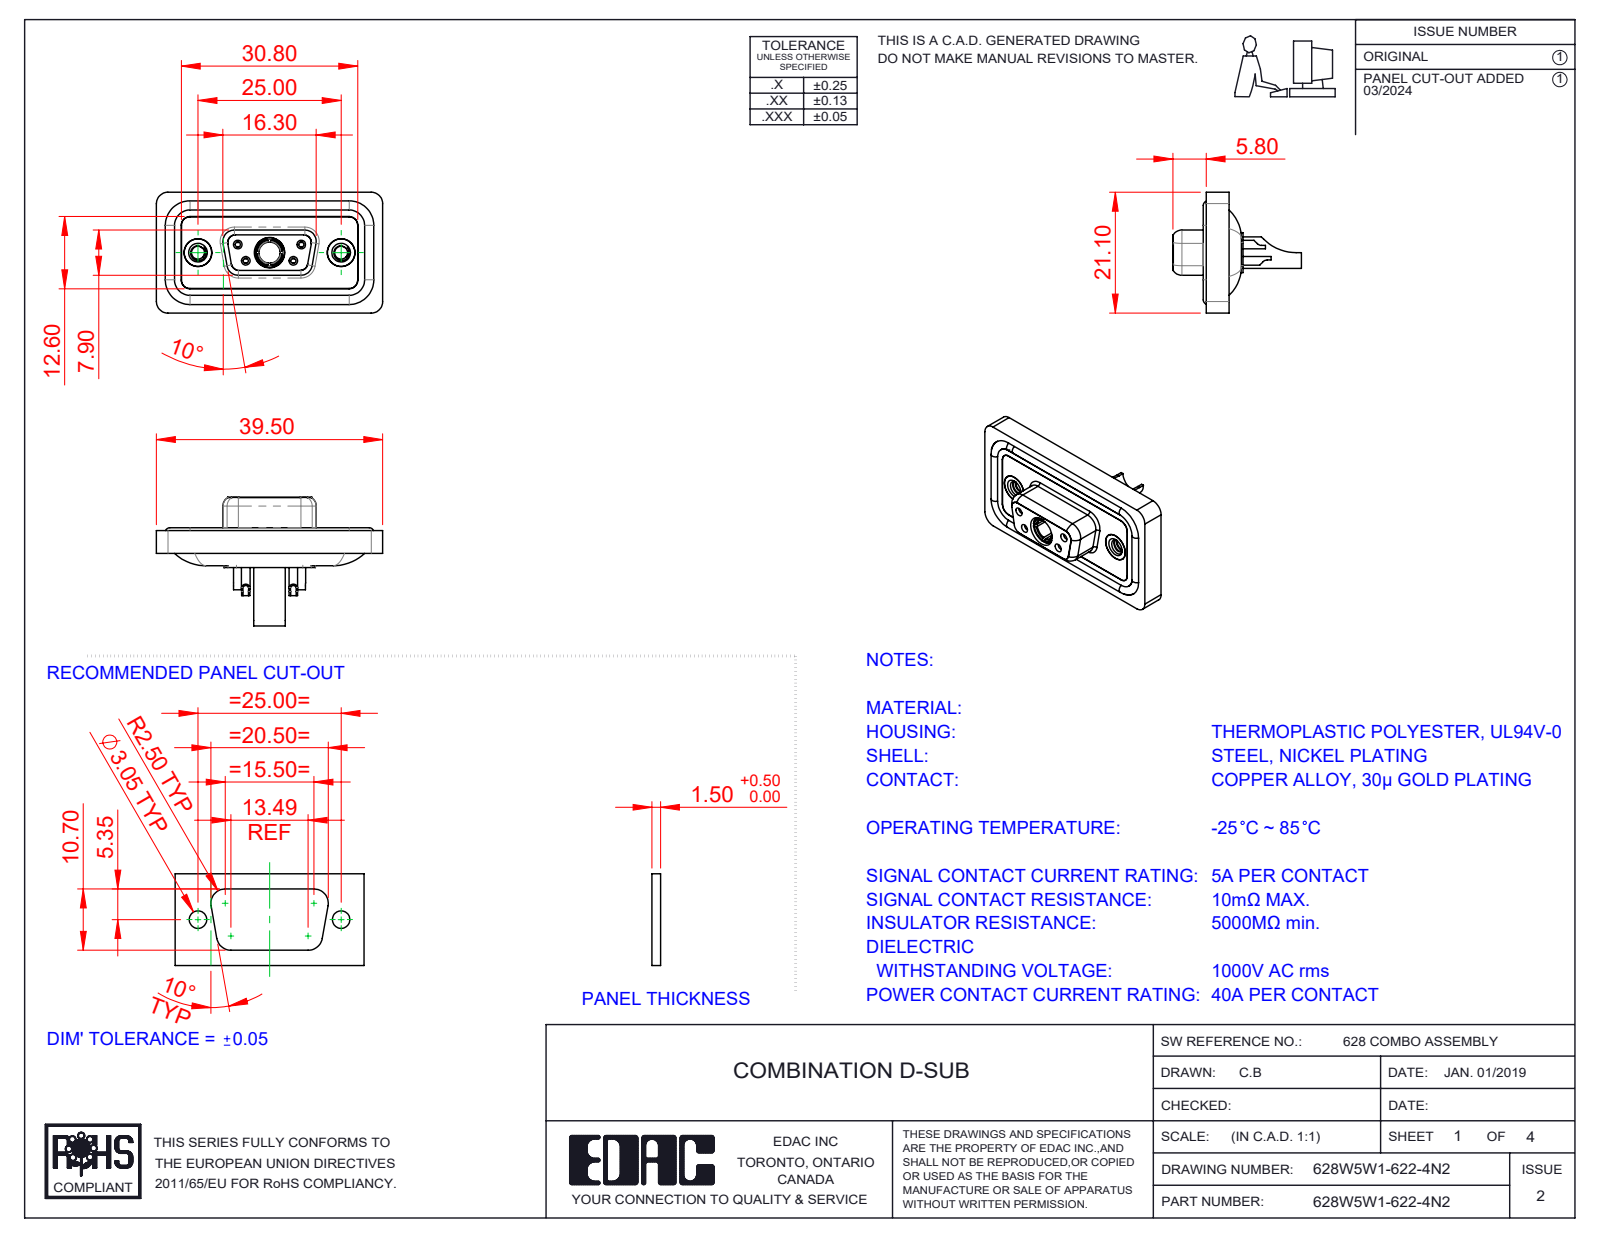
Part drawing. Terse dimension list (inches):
name: 628Combo Shell Front_09 Contacts; 628Combo Housing_5W1; 628Combo Shell Rear_09 Contacts; Power Socket_40A SC (+5 more)
written by: SolidWorks 2023 (CONFIG_CONTROL_DESIGN)
unit: in
bodies: 13 solids, 683 faces (204 planar, 296 cylindrical, 183 other)
size: 1.555 × 0.884 × 0.831
volume: 0.294 in³; area: 12.12 in²
holes: 4× ⌀0.035, 4× ⌀0.039, 4× ⌀0.043, 4× ⌀0.059, 4× ⌀0.079, 3× ⌀0.191, 2× ⌀0.063, 2× ⌀0.067, 2× ⌀0.089, 2× ⌀0.157, 2× ⌀0.159, 2× ⌀0.197
bosses: 6× ⌀0.063, 4× ⌀0.087, 2× ⌀0.195, 2× ⌀0.189, 1× ⌀0.217, 1× ⌀0.205, 1× ⌀0.195, 1× ⌀0.187
rounds: 22× R0.059, 18× R0.079, 8× R0.053, 8× R0.063, 6× R0.039, 4× R0.01, 4× R0.02, 4× R0.024
face distances: 0.016, 0.114, 0.043, 0.071, 0.063, 0.02, 0.222, 0.293, 0.211, 0.142
hole spacings: 0.124, 0.225, 0.28, 0.492, 0.713, 0.173, 0.173, 0.327
